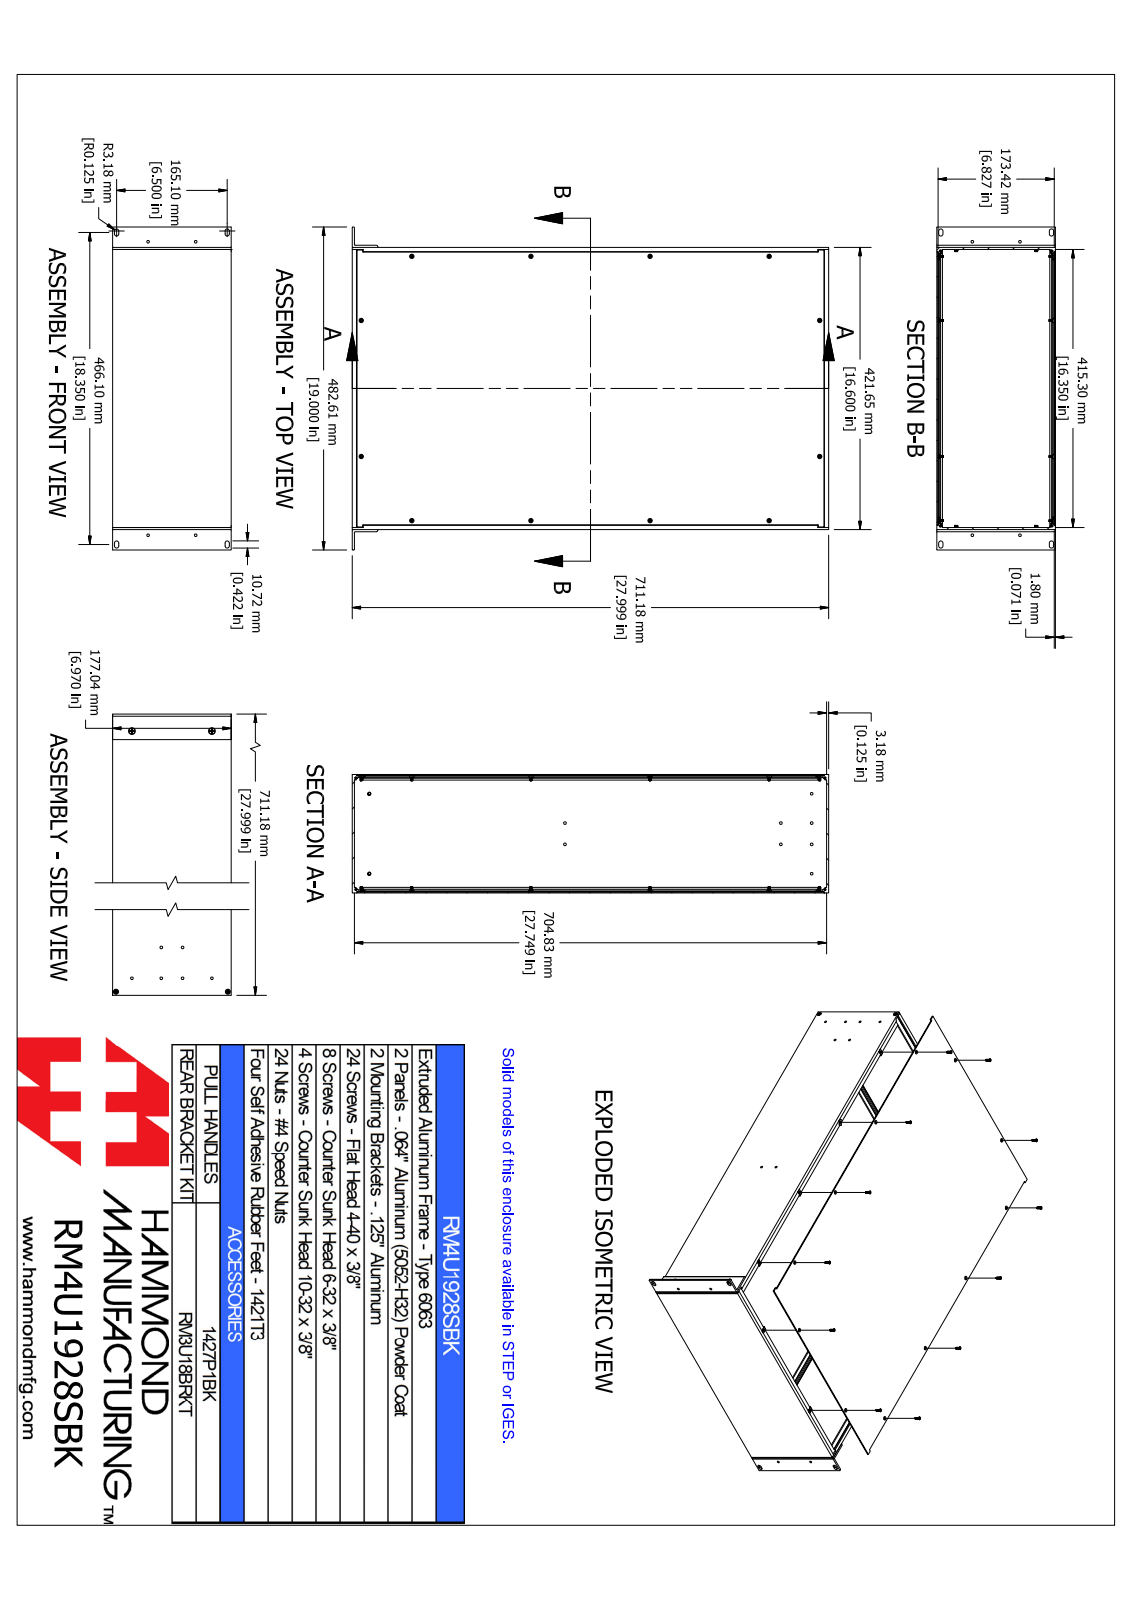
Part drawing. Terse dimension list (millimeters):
name: RM4U1928SBK
written by: SolidWorks 2021 (AUTOMOTIVE_DESIGN)
unit: mm
bodies: 68 solids, 2636 faces (1076 planar, 628 cylindrical, 932 other)
size: 711.2 × 482.6 × 177.1
volume: 2 550 000 mm³; area: 2 160 000 mm²
holes: 16× ⌀4, 12× ⌀4.1, 8× ⌀4.2, 6× ⌀4, 4× ⌀4, 4× ⌀4, 4× ⌀4.3, 2× ⌀5
bosses: 12× ⌀5.1, 12× ⌀2.8, 4× ⌀6, 4× ⌀3.5, 2× ⌀9.1, 2× ⌀4.8
rounds: 96× R0.3, 96× R0.6, 48× R0.2, 48× R0.4, 16× R0.4, 16× R1, 16× R1, 11× R0.9
face distances: 3.2, 175.2, 1.8, 177, 175.2, 1.8, 173.4, 418.5, 421.7, 415.3
hole spacings: 177.8, 433, 355.6, 531.4, 678.4, 122, 203.2, 270.8
